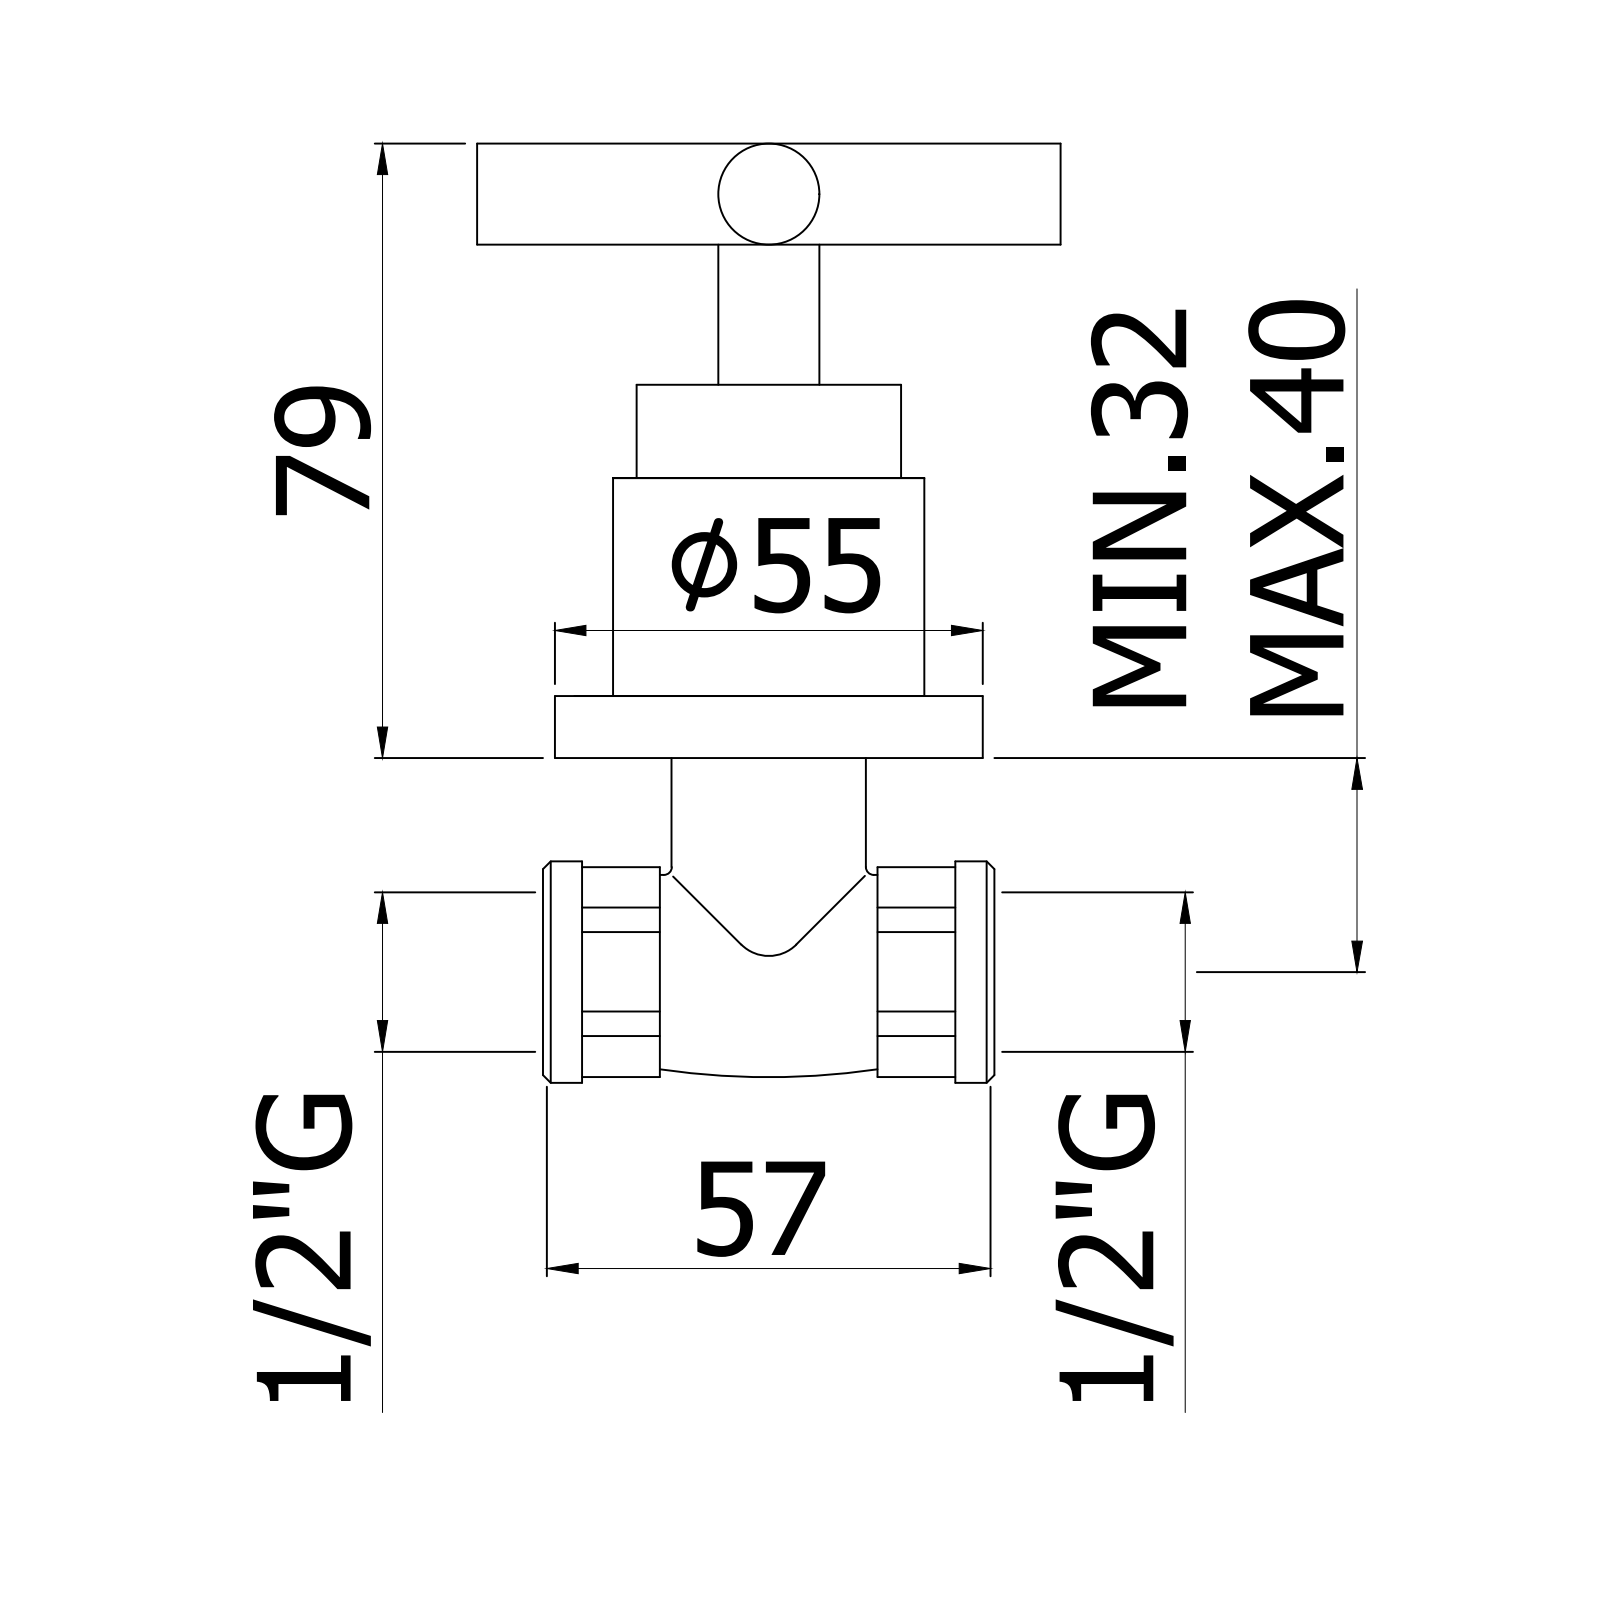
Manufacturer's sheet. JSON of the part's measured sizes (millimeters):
{"part_name": "QTV010CR", "step_written_by": "CREO PARAMETRIC BY PTC INC, 2020044 (CONFIG_CONTROL_DESIGN)", "units": "millimeters", "bodies": {"solids": 2, "faces": 401, "planar": 193, "cylindrical": 113, "other": 95}, "overall_size": [75.7, 61.1, 61.1], "volume_mm3": 74426, "surface_area_mm2": 29625, "round_holes": [[3.3, 1], [4.5, 1], [7, 1], [8, 1], [8.5, 1], [8.8, 1], [9.5, 1], [10.3, 1], [13.5, 1], [16.3, 1], [20, 1], [21, 1]], "round_bosses_or_shafts": [[12, 2], [55, 1], [49, 1], [39.8, 1], [36, 1], [34, 1], [27, 1], [24, 1]], "partial_cylinders_radius": [[0.1, 17], [0.5, 2], [1, 2], [3, 1], [9.4, 1]], "face_to_face_distances": [11, 5, 44.5, 6, 49.5, 38.5, 30, 39, 34, 28]}
